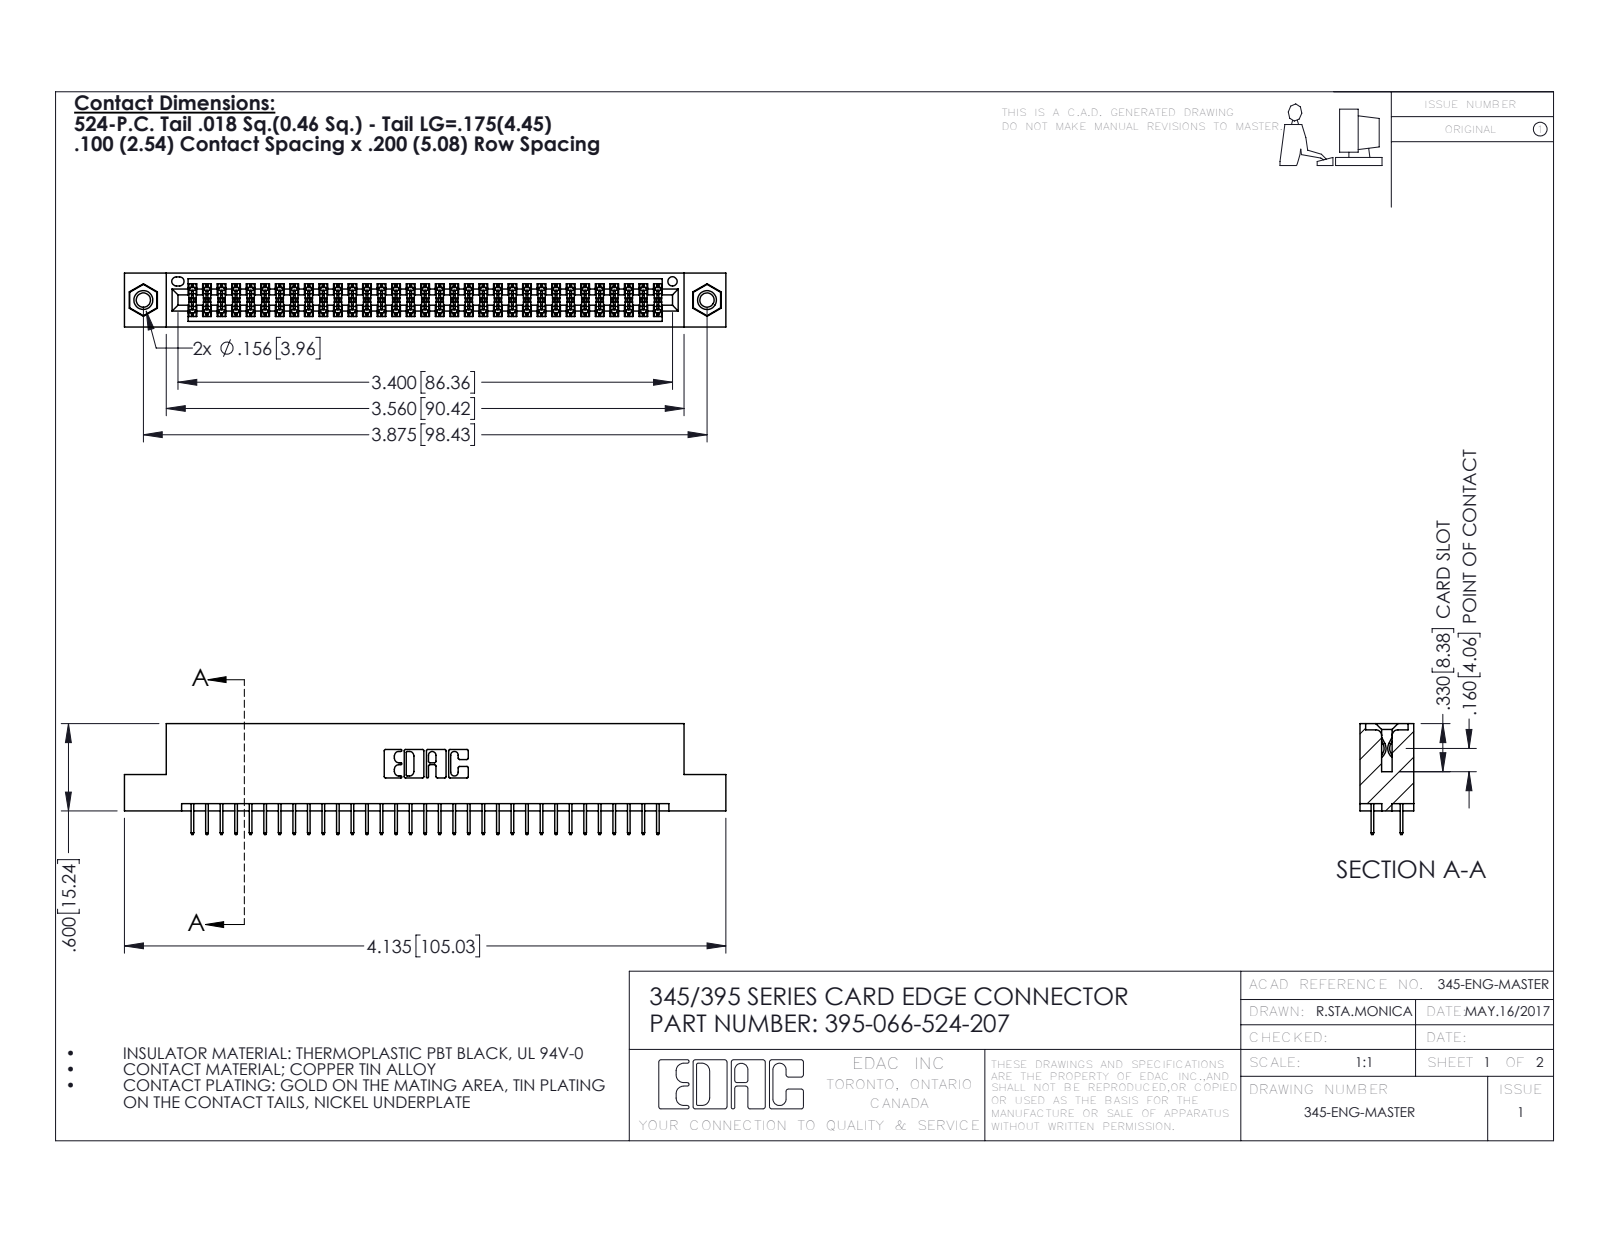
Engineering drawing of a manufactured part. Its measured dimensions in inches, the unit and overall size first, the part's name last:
Units: inches
Overall size (bounding box): 4.135 × 0.762 × 0.37
Round holes (diameter × count): ⌀0.098 ×2, ⌀0.125 ×2, ⌀0.156 ×2, ⌀0.064 ×1
Round bosses / shafts (diameter × count): ⌀0.155 ×2
Partial cylindrical surfaces — rounded edges, fillets, slot ends (radius × count): R0.006 ×99, R0.01 ×22, R0.007 ×6, R0.031 ×6, R0.026 ×3, R0.014 ×2, R0.019 ×2, R0.022 ×2
Main face-to-face distances: 0.072, 0.298, 0.2, 0.37, 0.098, 0.272, 0.025, 0.225, 0.072, 0.175
Hole centre spacings: 0.27, 3.64, 3.875
Volume: 0.611 in³ · Surface area: 22.29 in²
Bodies: 69 solids, 3750 faces (2686 planar, 1048 cylindrical, 16 other)
Part name (STEP PRODUCT): 345-250-001_345-250-005-103; 345-292-001_345-293-124; 345 Part_Flush Mounting Lugs - 0.156 Dia-TI; 395-066-524-207
STEP written by: SolidWorks 2016 (CONFIG_CONTROL_DESIGN)
